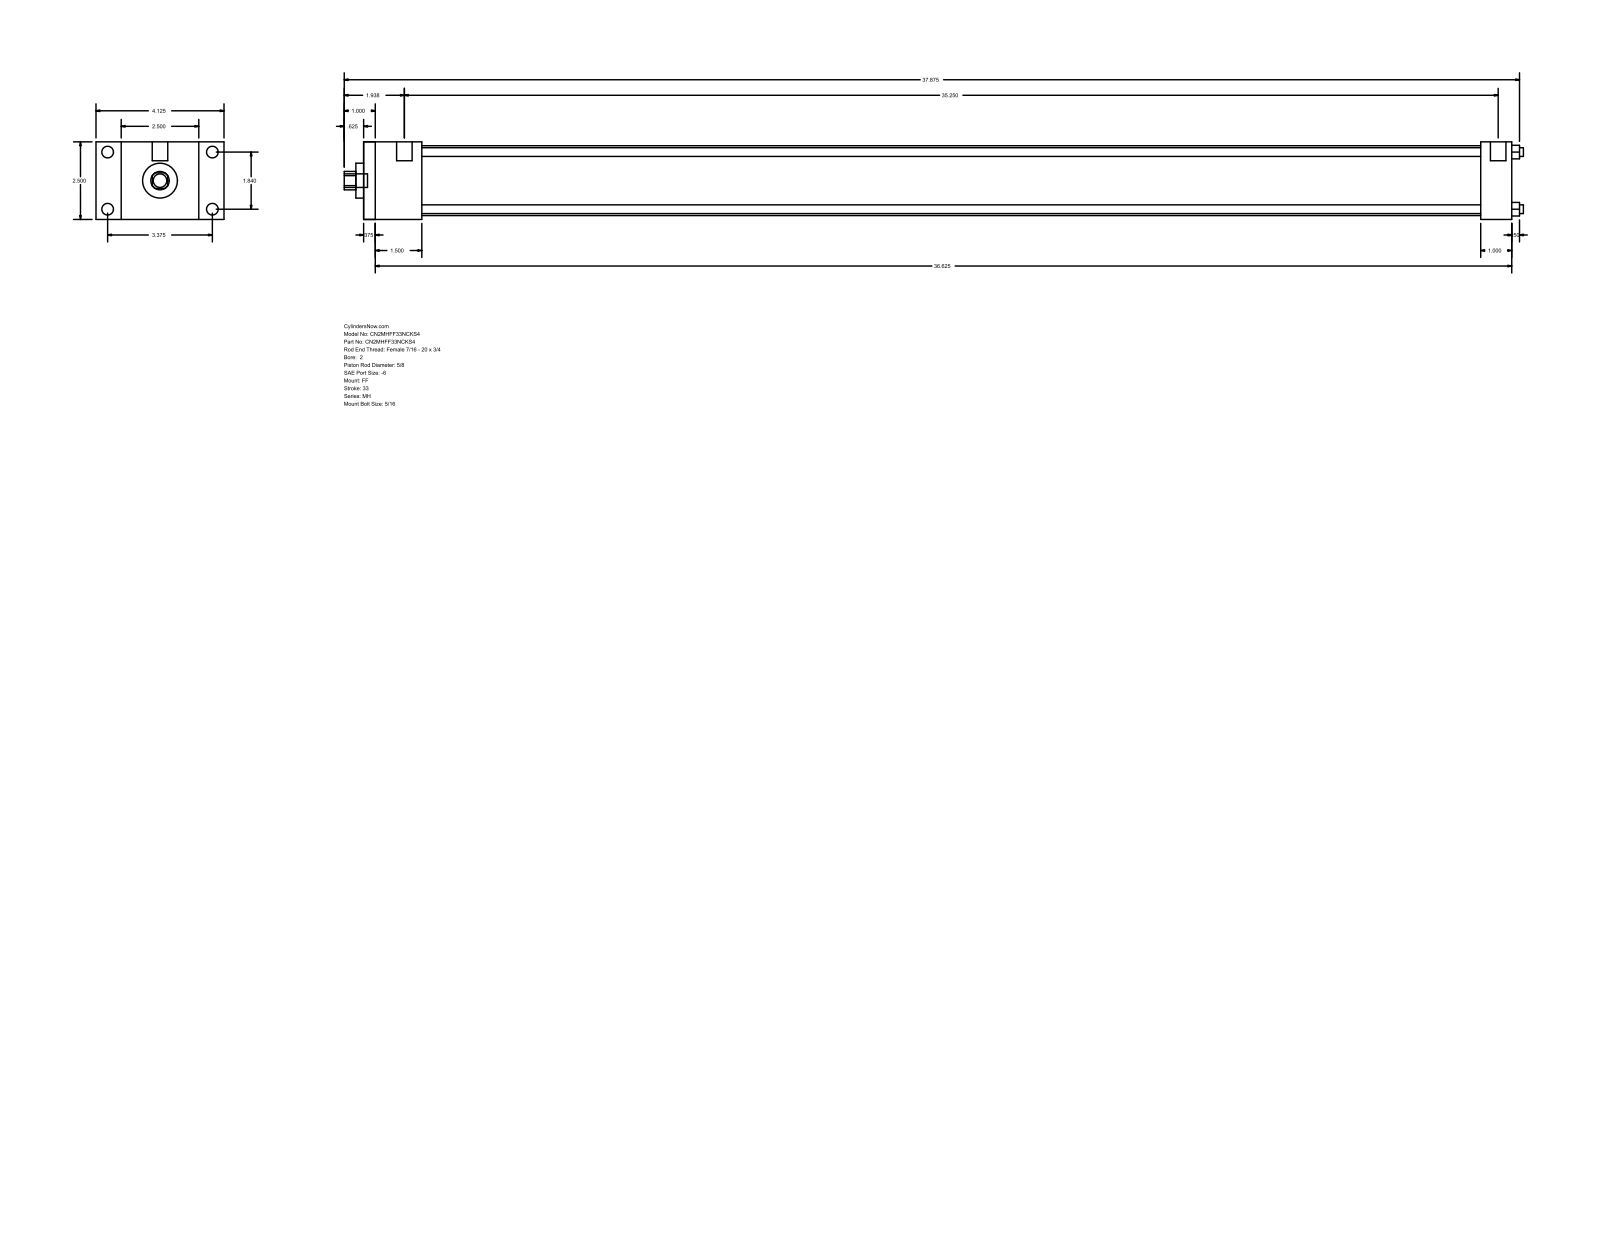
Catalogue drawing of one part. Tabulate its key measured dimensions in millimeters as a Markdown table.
| quantity | value |
| --- | --- |
| part name | MH_FF__0200_0.625 |
| STEP written by | GSSL Pune (CONFIG_CONTROL_DESIGN) |
| units | millimeters |
| bodies | 0 solids, 92 faces (64 planar, 28 cylindrical, 0 other) |
| overall size | 965.2 × 104.78 × 63.5 |
| round holes (diameter × count) | 7.14 × 4, 15.88 × 1, 28.57 × 1, 57.15 × 1 |
| round bosses / shafts (diameter × count) | 9.53 × 4, 5.56 × 4, 12.7 × 2, 11.11 × 1 |
| partial cylindrical surfaces (radius × count) | 7.54 × 1 |
| main face-to-face distances | 63.5, 939.79, 9.52, 930.27, 25.4, 38.1, 47.62, 914.39, 904.87, 866.77 |
| hole center spacings | 33.05, 46.74, 66.1 |
